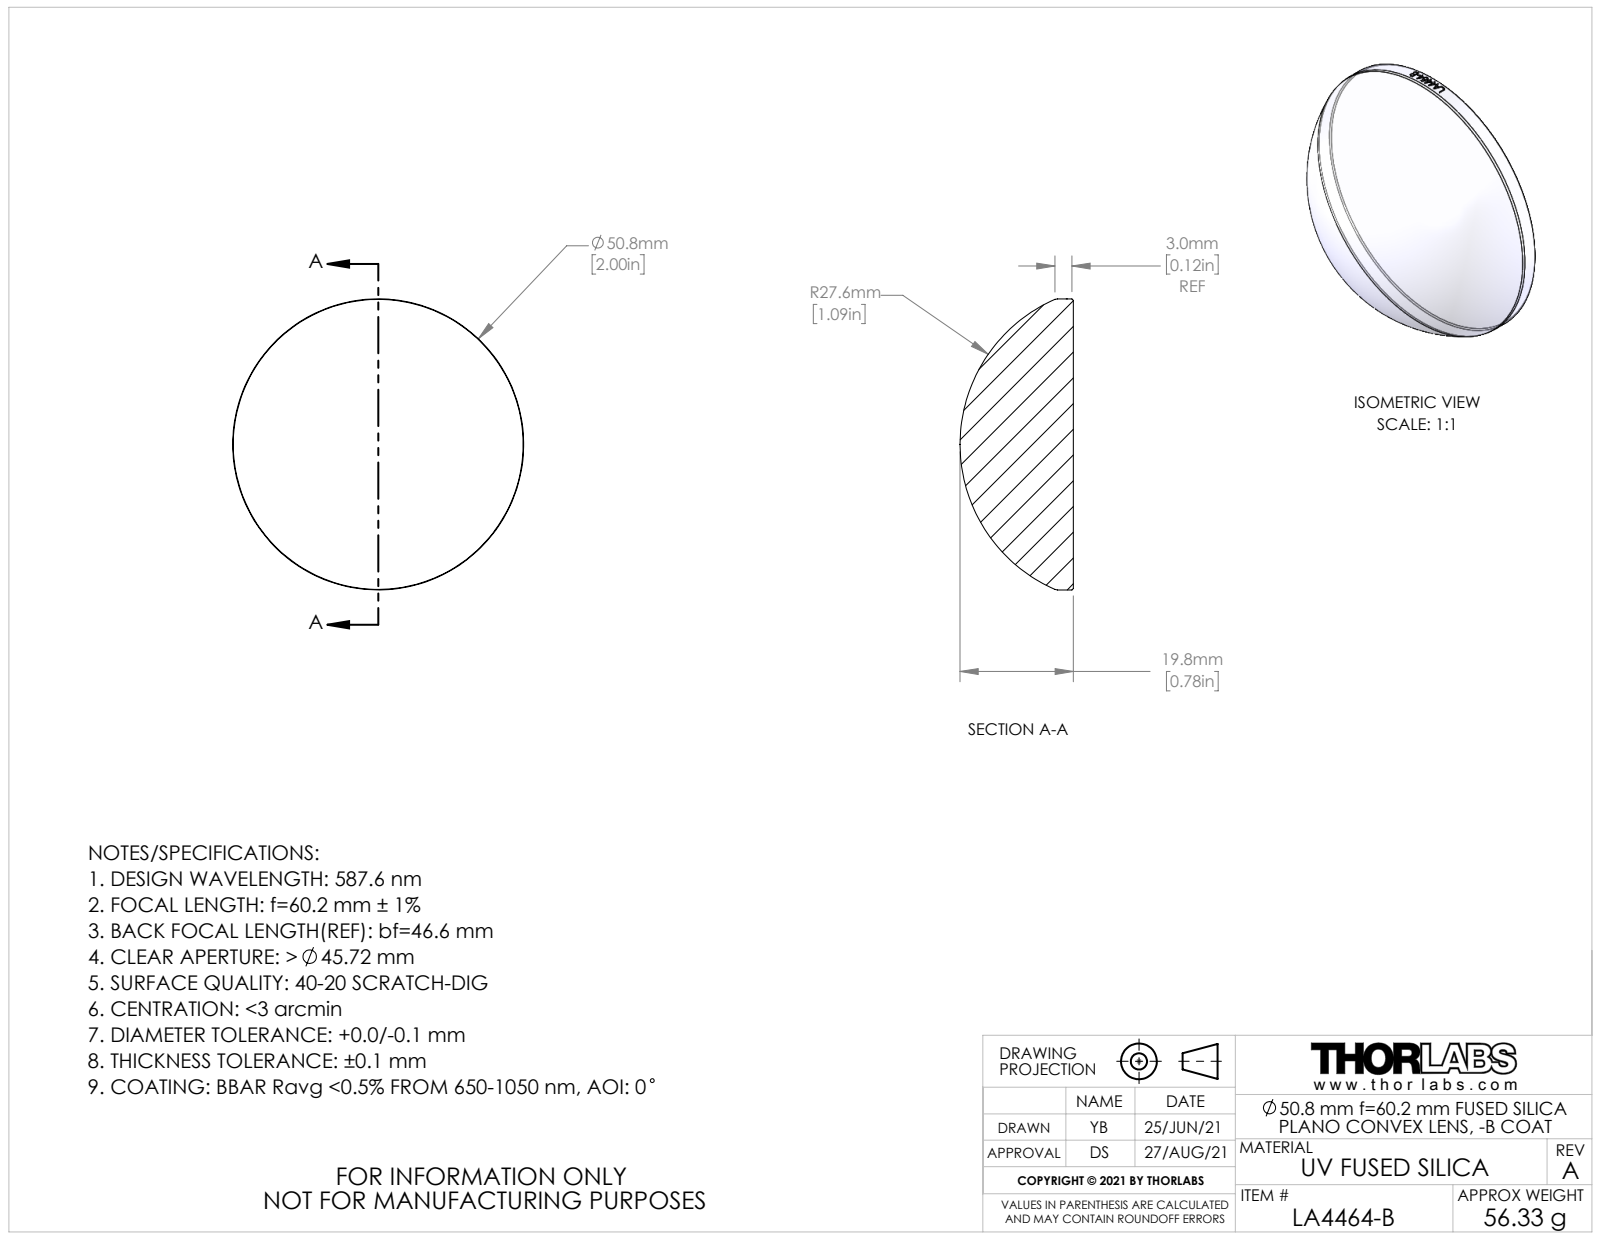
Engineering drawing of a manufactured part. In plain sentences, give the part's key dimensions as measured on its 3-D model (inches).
The part is named "CTN017902-E0W". Its 3-D file was written by "SolidWorks 2018 (AUTOMOTIVE_DESIGN)". It is 1 solid with 24 faces: 1 planar, 17 cylindrical and 6 other. Overall it measures 2 by 2 by 0.779 inches. Its volume is 1.56 cubic inches and its surface area 8.359 square inches. Round bosses or shafts: 1 of diameter 2.
